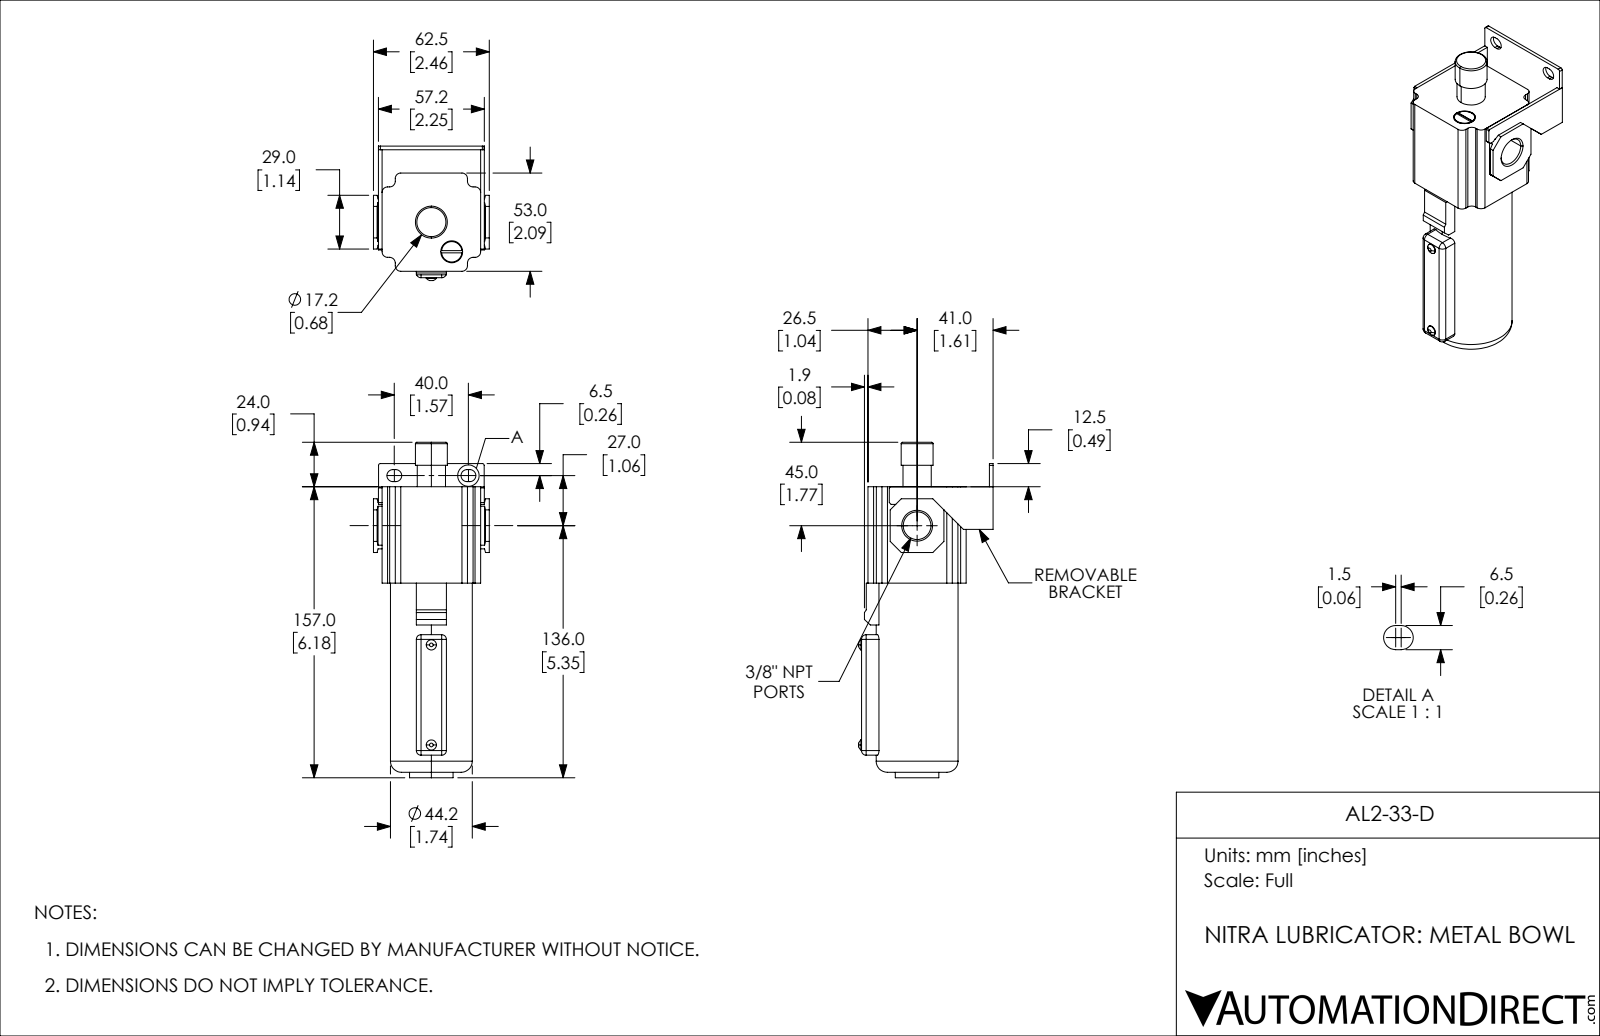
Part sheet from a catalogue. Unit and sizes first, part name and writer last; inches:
Units: inches
Overall size (bounding box): 7.126 × 2.854 × 2.461
Round holes (diameter × count): ⌀0.465 ×1, ⌀0.589 ×1
Round bosses / shafts (diameter × count): ⌀0.217 ×2, ⌀1.74 ×1, ⌀0.925 ×1, ⌀0.677 ×1, ⌀0.598 ×1, ⌀0.433 ×1
Partial cylindrical surfaces — rounded edges, fillets, slot ends (radius × count): R0.118 ×12, R0.098 ×8, R0.128 ×4, R0.039 ×2
Main face-to-face distances: 0.079, 0.492, 0.571, 2.657, 2.579, 2.087, 2.173, 2.094, 0.728, 0.807
Volume: 19.24 in³ · Surface area: 64.89 in²
Bodies: 1 solid, 162 faces (100 planar, 46 cylindrical, 16 other)
Part name (STEP PRODUCT): AL2-33-D
STEP written by: SolidWorks 2019 (CONFIG_CONTROL_DESIGN)
